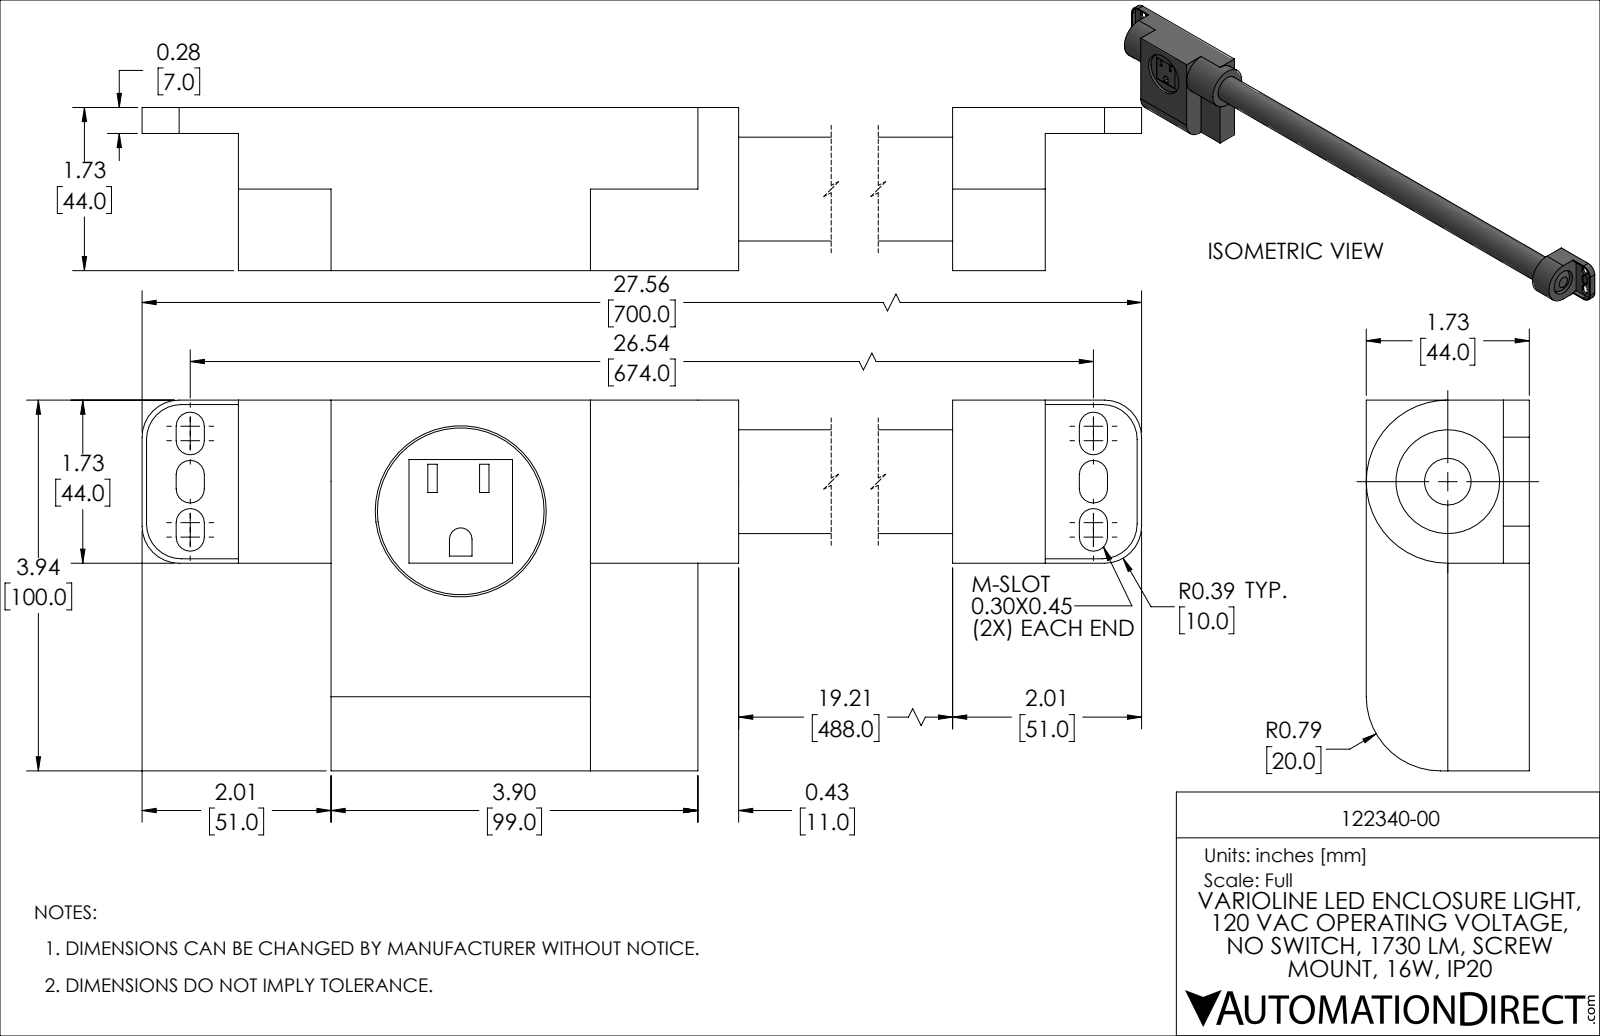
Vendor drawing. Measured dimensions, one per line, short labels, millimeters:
name: PRODUCT_NAME_1
written by: ACIS (AUTOMOTIVE_DESIGN_CC2)
unit: mm
bodies: 1 solid, 113 faces (69 planar, 38 cylindrical, 6 other)
size: 700 × 100 × 44
volume: 786 249 mm³; area: 106 932 mm²
holes: 1× ⌀28, 1× ⌀46.15
bosses: 1× ⌀45, 1× ⌀44
rounds: 12× R3.8, 4× R9.4, 4× R10, 1× R3.05, 1× R20
face distances: 44, 22, 100, 623, 25, 41.6, 2.4, 19.6, 99, 70
